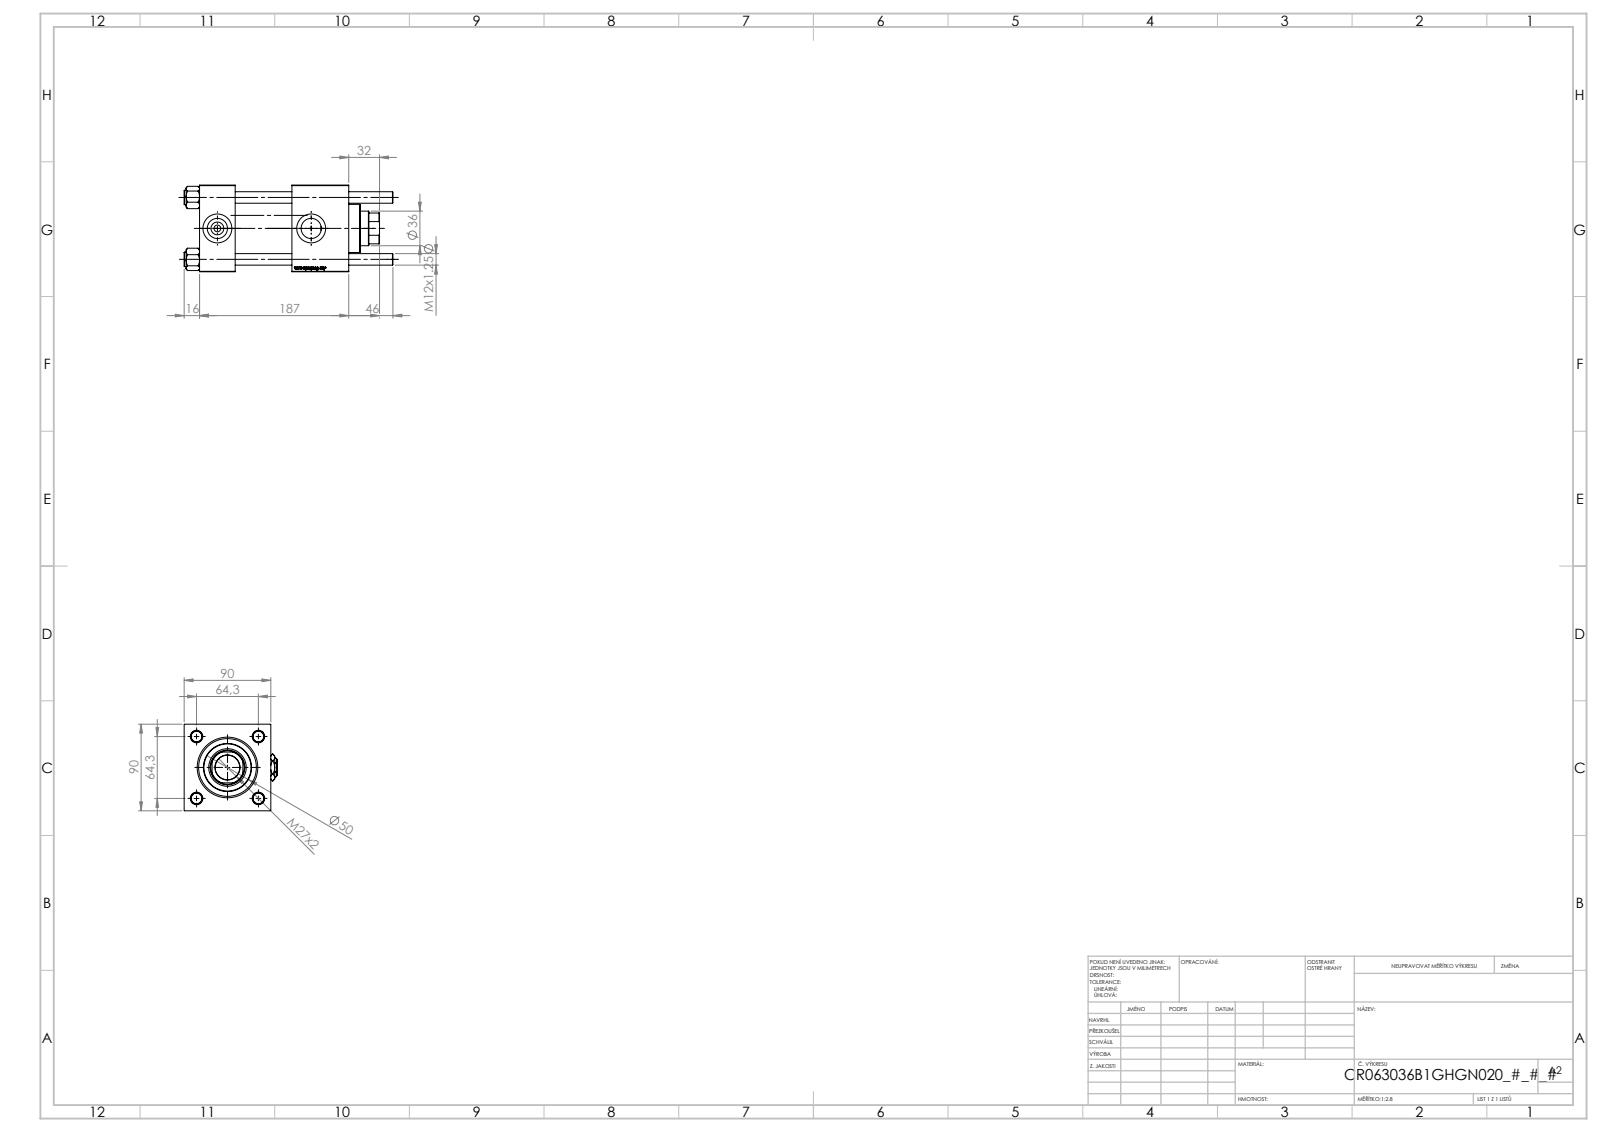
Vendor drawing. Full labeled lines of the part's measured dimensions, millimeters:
Part name (STEP PRODUCT): V215CR_B-1; NUT_M5_B; V215_VC_A; V215CR_B_TYCINKA (+2 more)
STEP written by: SolidWorks 2019 (CONFIG_CONTROL_DESIGN)
Units: millimetres
Bodies: 12 solids, 1205 faces (455 planar, 82 cylindrical, 668 other)
Overall size (bounding box): 217 × 97 × 90
Volume: 997 988 mm³ · Surface area: 202 240 mm²
Round holes (diameter × count): ⌀12 ×4, ⌀7 ×2, ⌀20.96 ×2, ⌀30 ×2, ⌀25.5 ×1, ⌀36 ×1, ⌀39 ×1, ⌀50 ×1, ⌀60 ×1, ⌀63 ×1
Round bosses / shafts (diameter × count): ⌀15 ×4, ⌀69 ×1
Partial cylindrical surfaces — rounded edges, fillets, slot ends (radius × count): R17.5 ×1
Main face-to-face distances: 90, 59, 37, 118, 155, 96, 126.3, 89.3, 30.3, 28.7
Hole centre spacings: 45.47, 64.3, 90.93, 97.5
